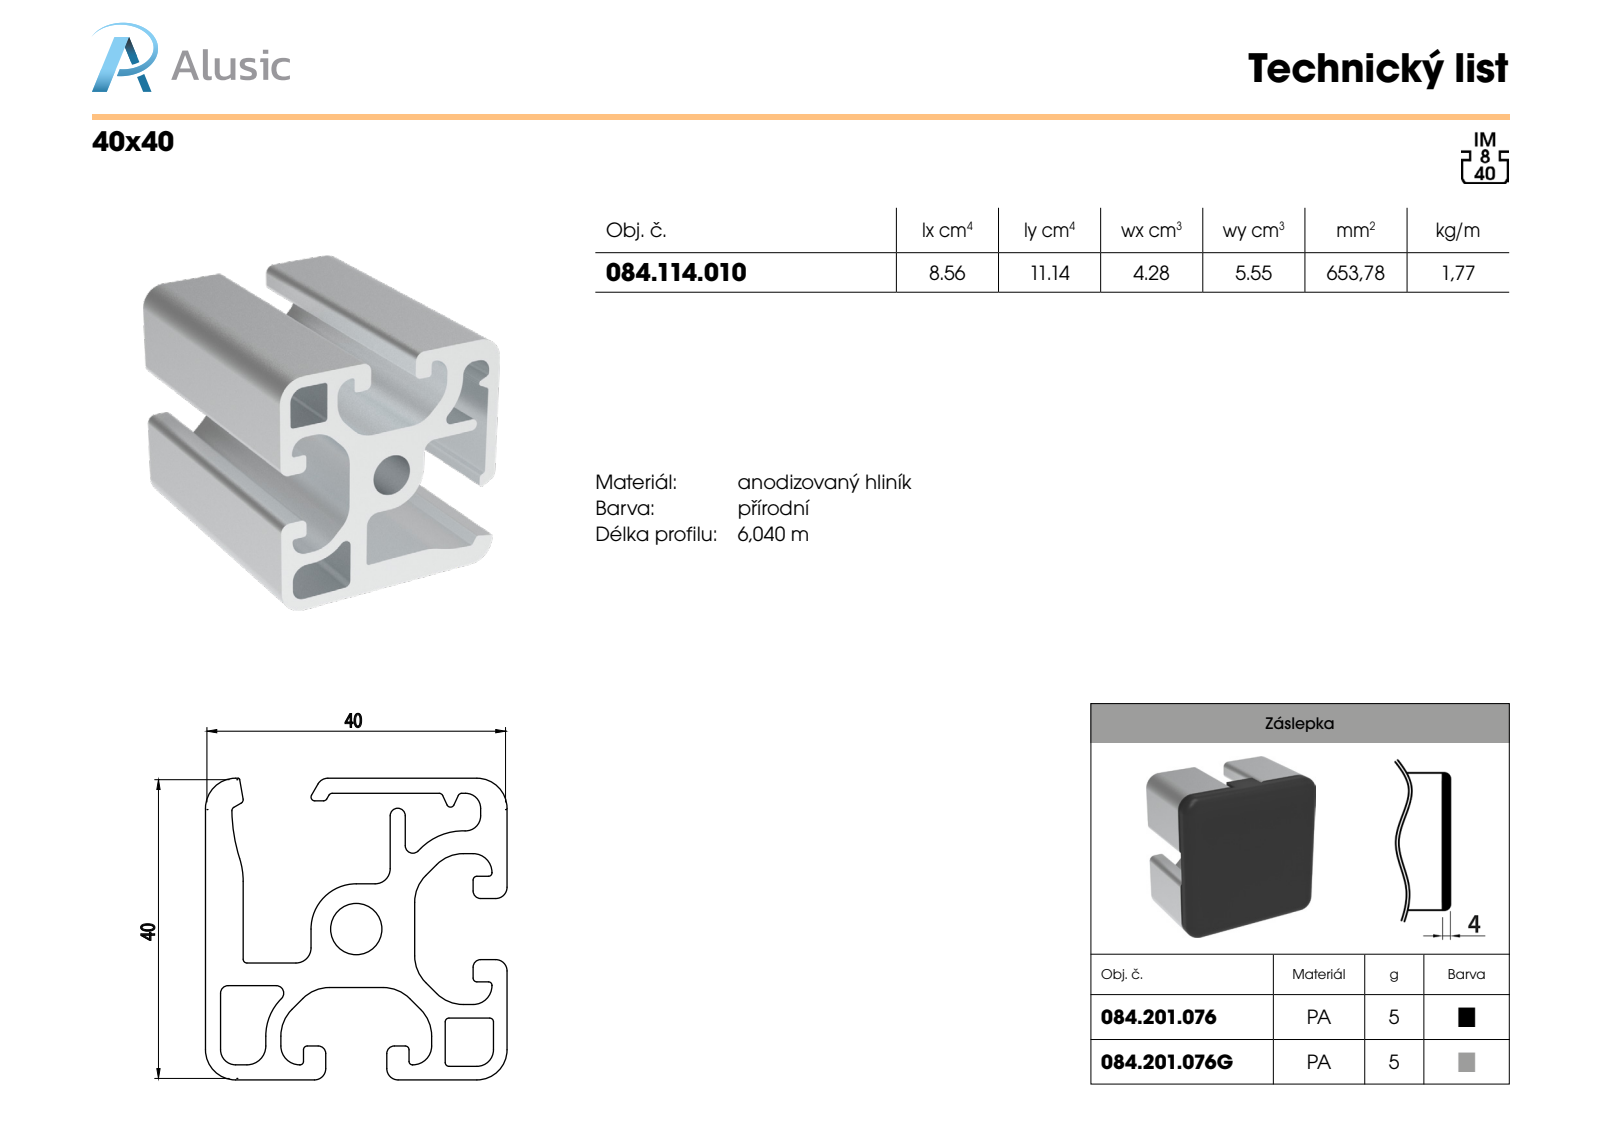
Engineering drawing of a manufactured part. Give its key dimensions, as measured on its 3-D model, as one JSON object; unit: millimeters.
{"part_name": "084.114.010", "step_written_by": "SolidWorks 2018 (AUTOMOTIVE_DESIGN)", "units": "millimeters", "bodies": {"solids": 1, "faces": 126, "planar": 60, "cylindrical": 66, "other": 0}, "overall_size": [100, 40, 40], "volume_mm3": 65378, "surface_area_mm2": 43809, "round_holes": [[6.8, 1]], "partial_cylinders_radius": [[0.5, 16], [1, 8], [5, 8], [1.5, 5], [2, 5], [2.5, 5], [0.45, 4], [4, 4]], "face_to_face_distances": [40, 2, 38, 3, 24.5, 22.5, 12.25, 25.75, 27.75, 15.5]}
